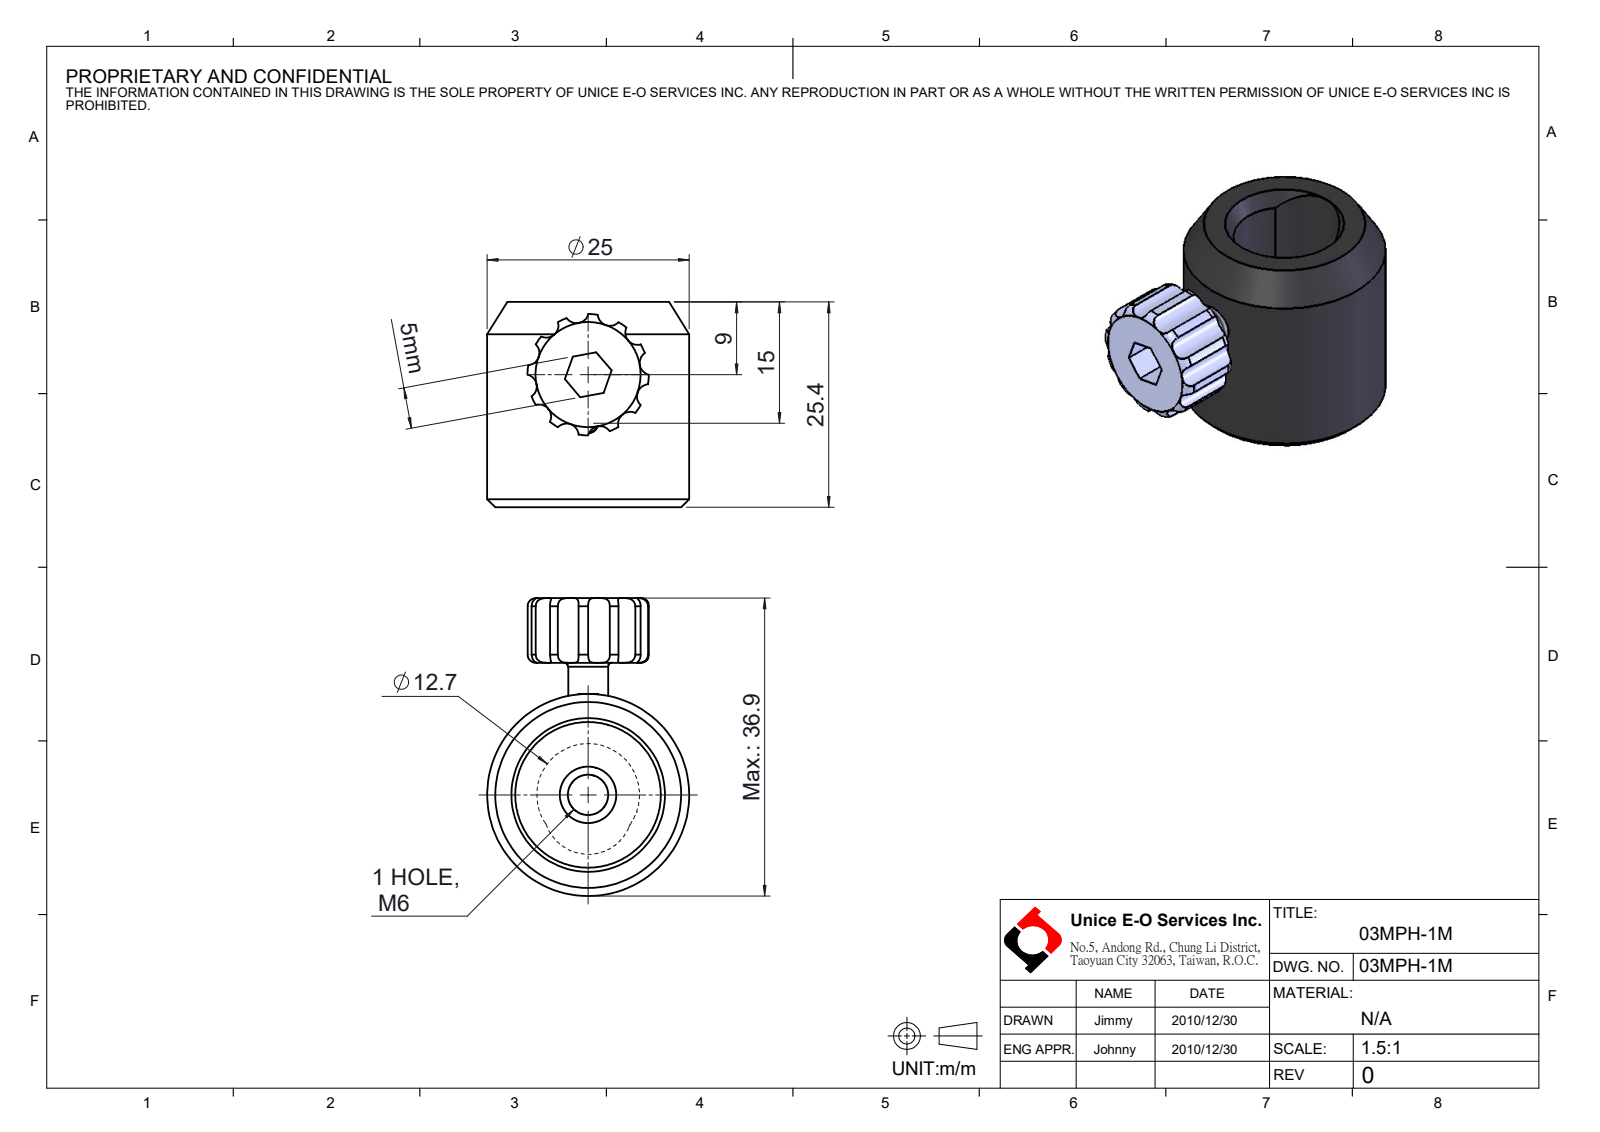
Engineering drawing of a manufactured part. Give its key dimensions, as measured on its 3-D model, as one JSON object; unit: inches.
{"part_name": "03MPH-1M", "step_written_by": "SolidWorks 2016 (CONFIG_CONTROL_DESIGN)", "units": "inches", "bodies": {"solids": 0, "faces": 101, "planar": 17, "cylindrical": 44, "other": 40}, "overall_size": [1.451, 1, 0.984], "round_holes": [[0.197, 2], [0.098, 1], [0.748, 1]], "round_bosses_or_shafts": [[0.984, 1], [0.194, 1]], "partial_cylinders_radius": [[0.059, 12], [0.217, 1], [0.25, 1], [0.295, 1]], "face_to_face_distances": [1, 0.315, 0.165, 0.15, 0.201, 0.201, 0.152, 0.317, 0.467, 0.059], "hole_center_spacings": [0.236]}
